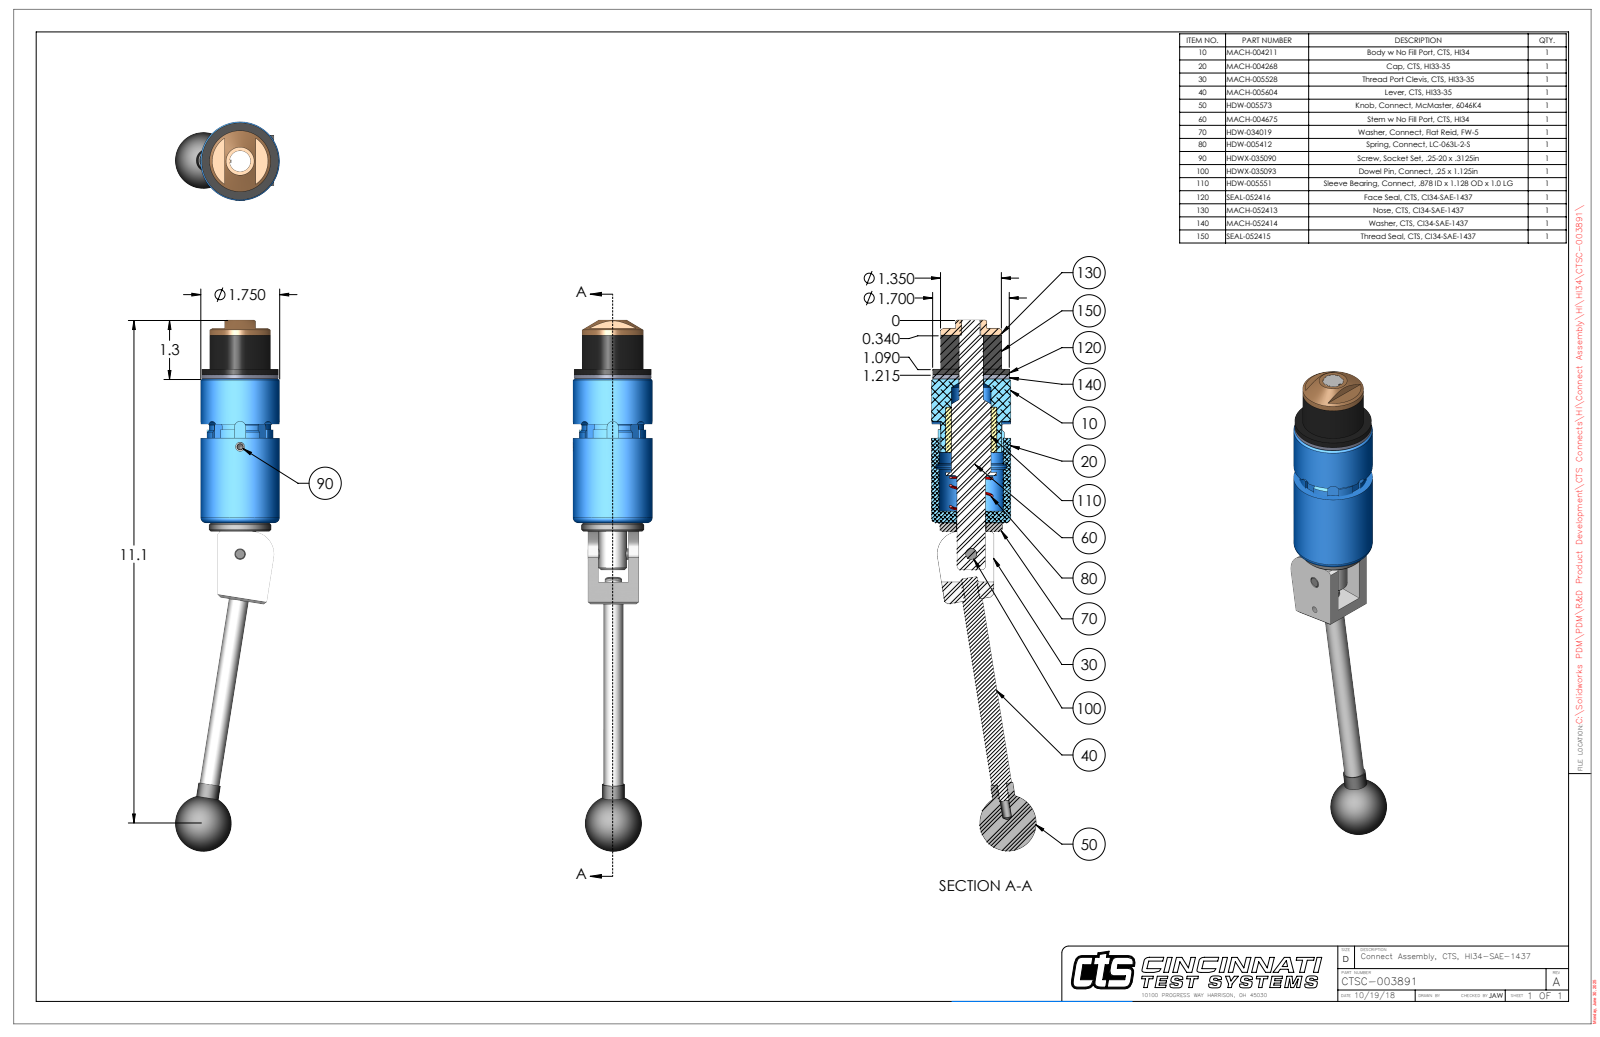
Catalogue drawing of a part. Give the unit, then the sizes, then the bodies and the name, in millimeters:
Units: millimetres
Overall size (bounding box): 299 × 58.7 × 44.5
Round holes (diameter × count): ⌀5.1 ×2, ⌀3.8 ×1, ⌀6.3 ×1, ⌀6.4 ×1, ⌀8 ×1, ⌀10.7 ×1, ⌀13.5 ×1, ⌀13.9 ×1, ⌀16.1 ×1, ⌀16.7 ×1
Round bosses / shafts (diameter × count): ⌀12.7 ×2, ⌀11.2 ×2, ⌀6.4 ×2, ⌀44.5 ×1, ⌀43.2 ×1, ⌀35.1 ×1, ⌀34.3 ×1, ⌀15.9 ×1
Partial cylindrical surfaces — rounded edges, fillets, slot ends (radius × count): R3.2 ×4, R0.7 ×2, R12.7 ×1, R17.7 ×1, R18 ×1, R18.9 ×1, R20.8 ×1
Main face-to-face distances: 2.4, 5.6, 3.2, 80.9, 19.1, 22.2, 24.6, 105.5, 86.5, 83.3
Hole centre spacings: 18.8, 60.4, 79.1
Volume: 207 000 mm³ · Surface area: 49 910 mm²
Bodies: 10 solids, 274 faces (102 planar, 115 cylindrical, 57 other)
Part name (STEP PRODUCT): CTSC-003891
STEP written by: SolidWorks 2023 (AUTOMOTIVE_DESIGN)
